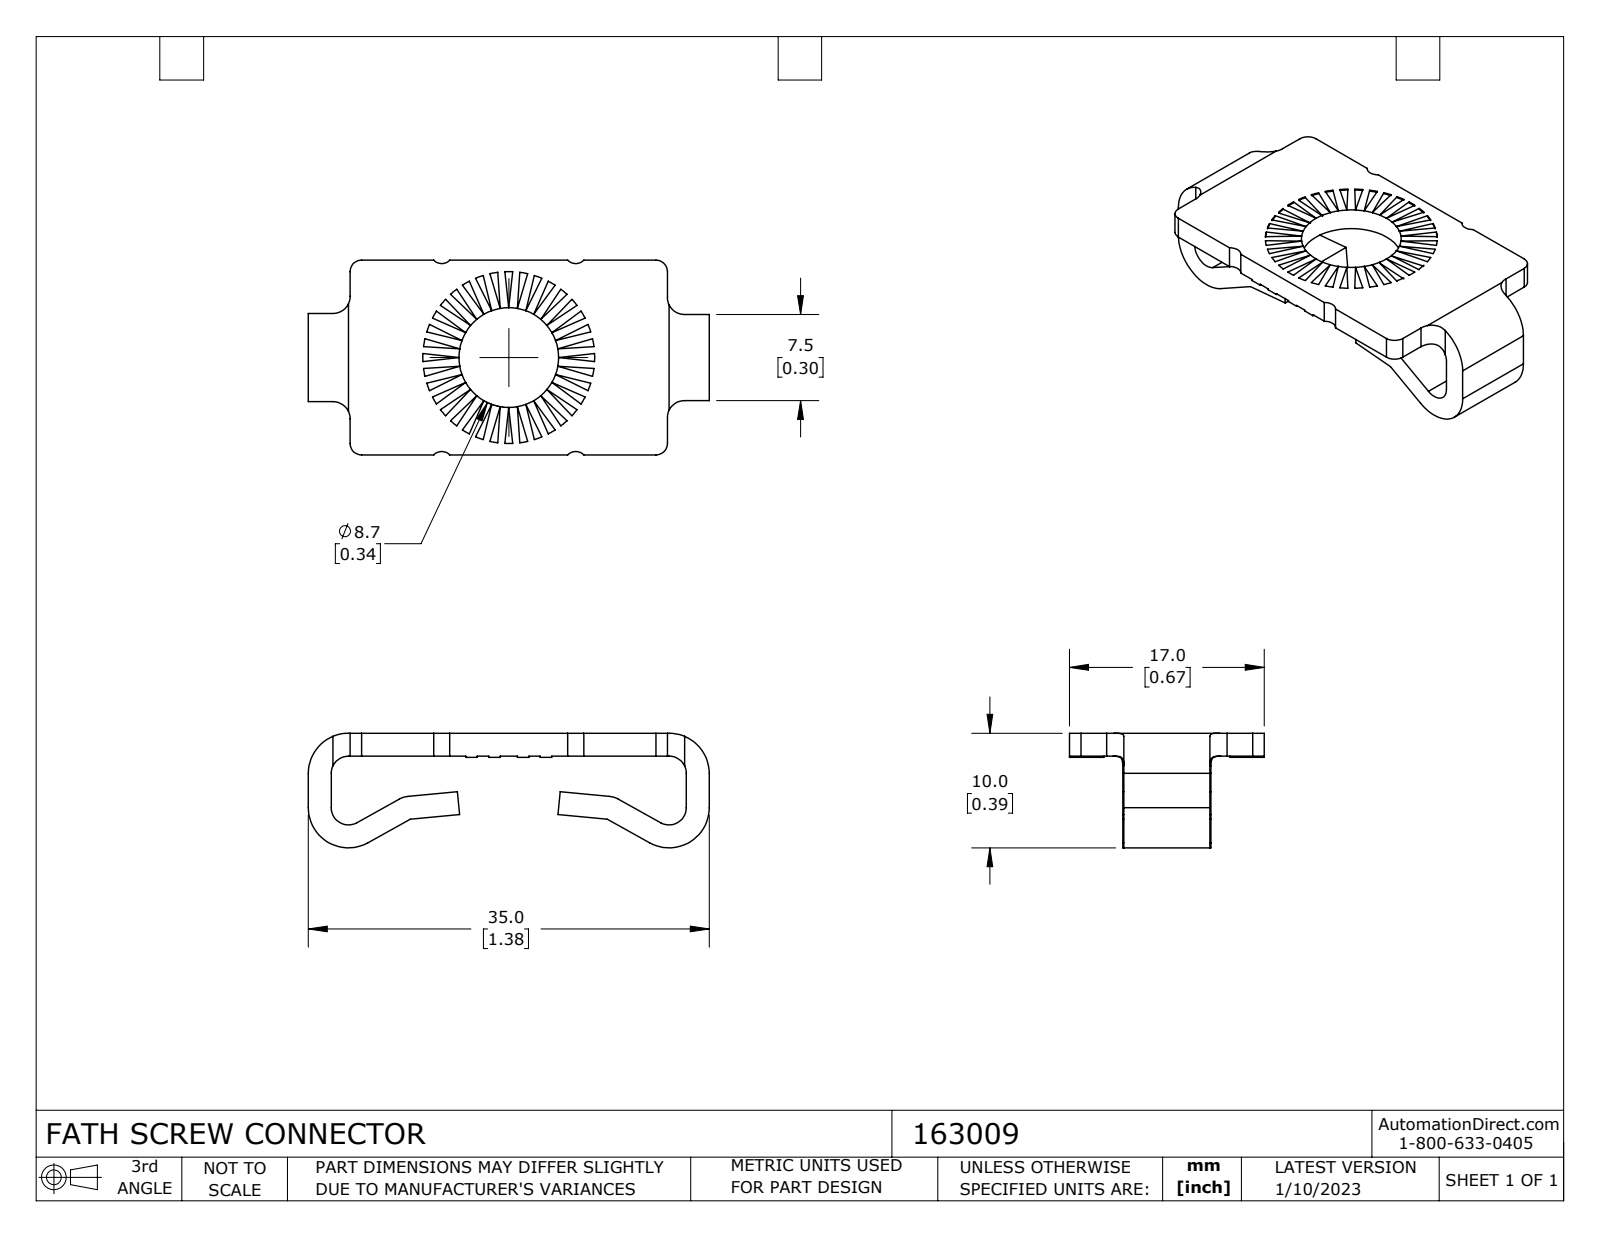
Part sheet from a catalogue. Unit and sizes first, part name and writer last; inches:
Units: inches
Overall size (bounding box): 1.378 × 0.669 × 0.394
Round holes (diameter × count): ⌀0.343 ×1
Partial cylindrical surfaces — rounded edges, fillets, slot ends (radius × count): R0.059 ×8, R0.038 ×4, R0.039 ×4, R0.138 ×4, R0.079 ×2, R0.295 ×1
Main face-to-face distances: 0.079, 0.183, 0.187, 0.482, 0.486, 0.299, 0.669, 1.299, 0.295, 0.075
Volume: 0.09 in³ · Surface area: 2.899 in²
Bodies: 1 solid, 161 faces (98 planar, 63 cylindrical, 0 other)
Part name (STEP PRODUCT): 163009
STEP written by: SolidWorks 2021 (CONFIG_CONTROL_DESIGN)
